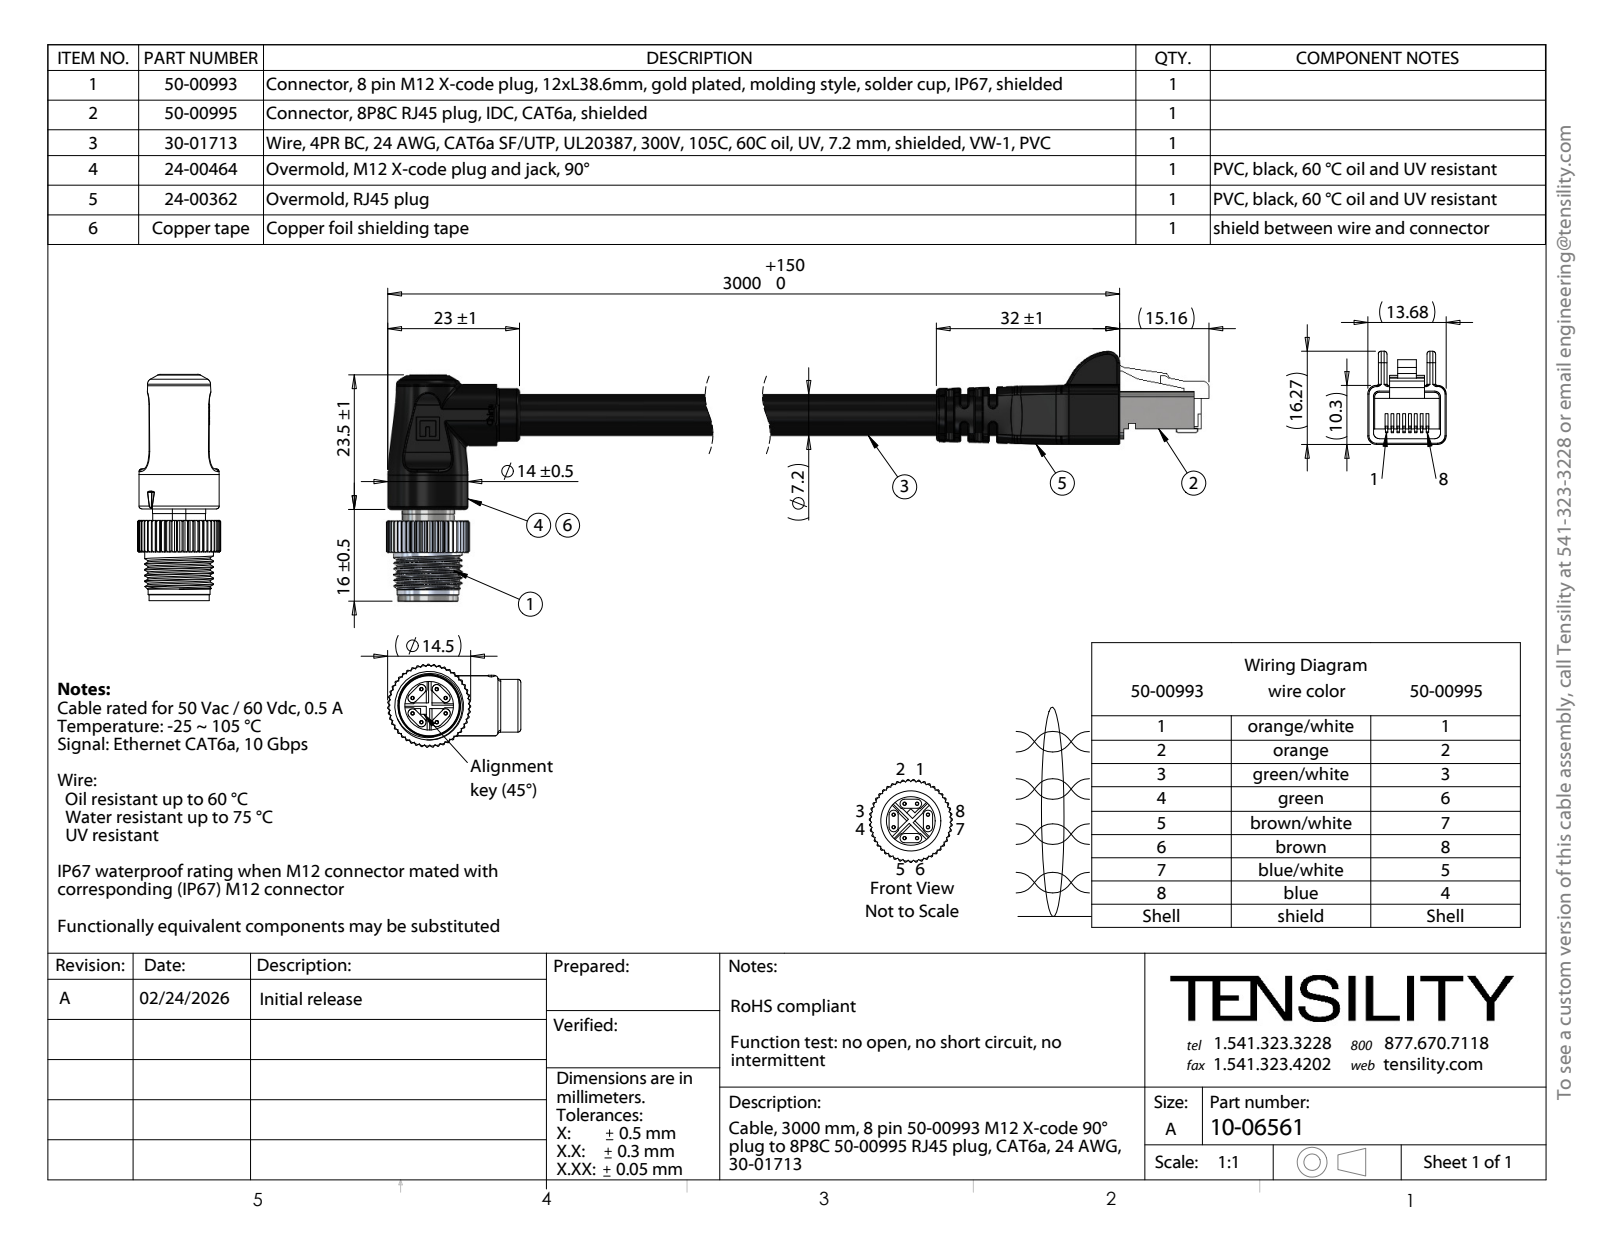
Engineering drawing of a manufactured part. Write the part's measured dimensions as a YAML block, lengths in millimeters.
part_name: "50-00995; 24-00362; 50-00993-04_默认; 30-01713_blunt cut (+7 more)"
step_written_by: "SolidWorks 2025 (CONFIG_CONTROL_DESIGN)"
units: millimeters
bodies: {solids: 95, faces: 2077, planar: 843, cylindrical: 677, other: 557}
overall_size: [210.35, 43.62, 14.49]
volume: 15667
surface_area: 49597
round_holes:
  - {diameter: 0.2, count: 56}
  - {diameter: 0.6, count: 8}
  - {diameter: 1.2, count: 8}
  - {diameter: 2, count: 1}
  - {diameter: 2.5, count: 1}
  - {diameter: 5.03, count: 1}
  - {diameter: 5.25, count: 1}
  - {diameter: 5.65, count: 1}
  - {diameter: 5.75, count: 1}
  - {diameter: 7.5, count: 1}
  - {diameter: 8.5, count: 1}
  - {diameter: 9.07, count: 1}
round_bosses_or_shafts:
  - {diameter: 1.4, count: 8}
  - {diameter: 1.15, count: 8}
  - {diameter: 1.05, count: 8}
  - {diameter: 0.8, count: 8}
  - {diameter: 9.2, count: 2}
  - {diameter: 14, count: 1}
  - {diameter: 12, count: 1}
  - {diameter: 11, count: 1}
partial_cylinders:
  - {radius: 0.5, count: 14}
  - {radius: 1, count: 13}
  - {radius: 0.1, count: 12}
  - {radius: 0.2, count: 11}
  - {radius: 0.8, count: 10}
  - {radius: 0.62, count: 8}
  - {radius: 1.5, count: 8}
  - {radius: 2.17, count: 4}
face_to_face_distances: [0.5, 1, 0.99, 0.98, 2, 1.25, 5, 3.9, 3.75, 2.7]
hole_center_spacings: [0.35, 1.61, 1.78, 0.41, 1.06, 1.43, 1.93, 2.48]
